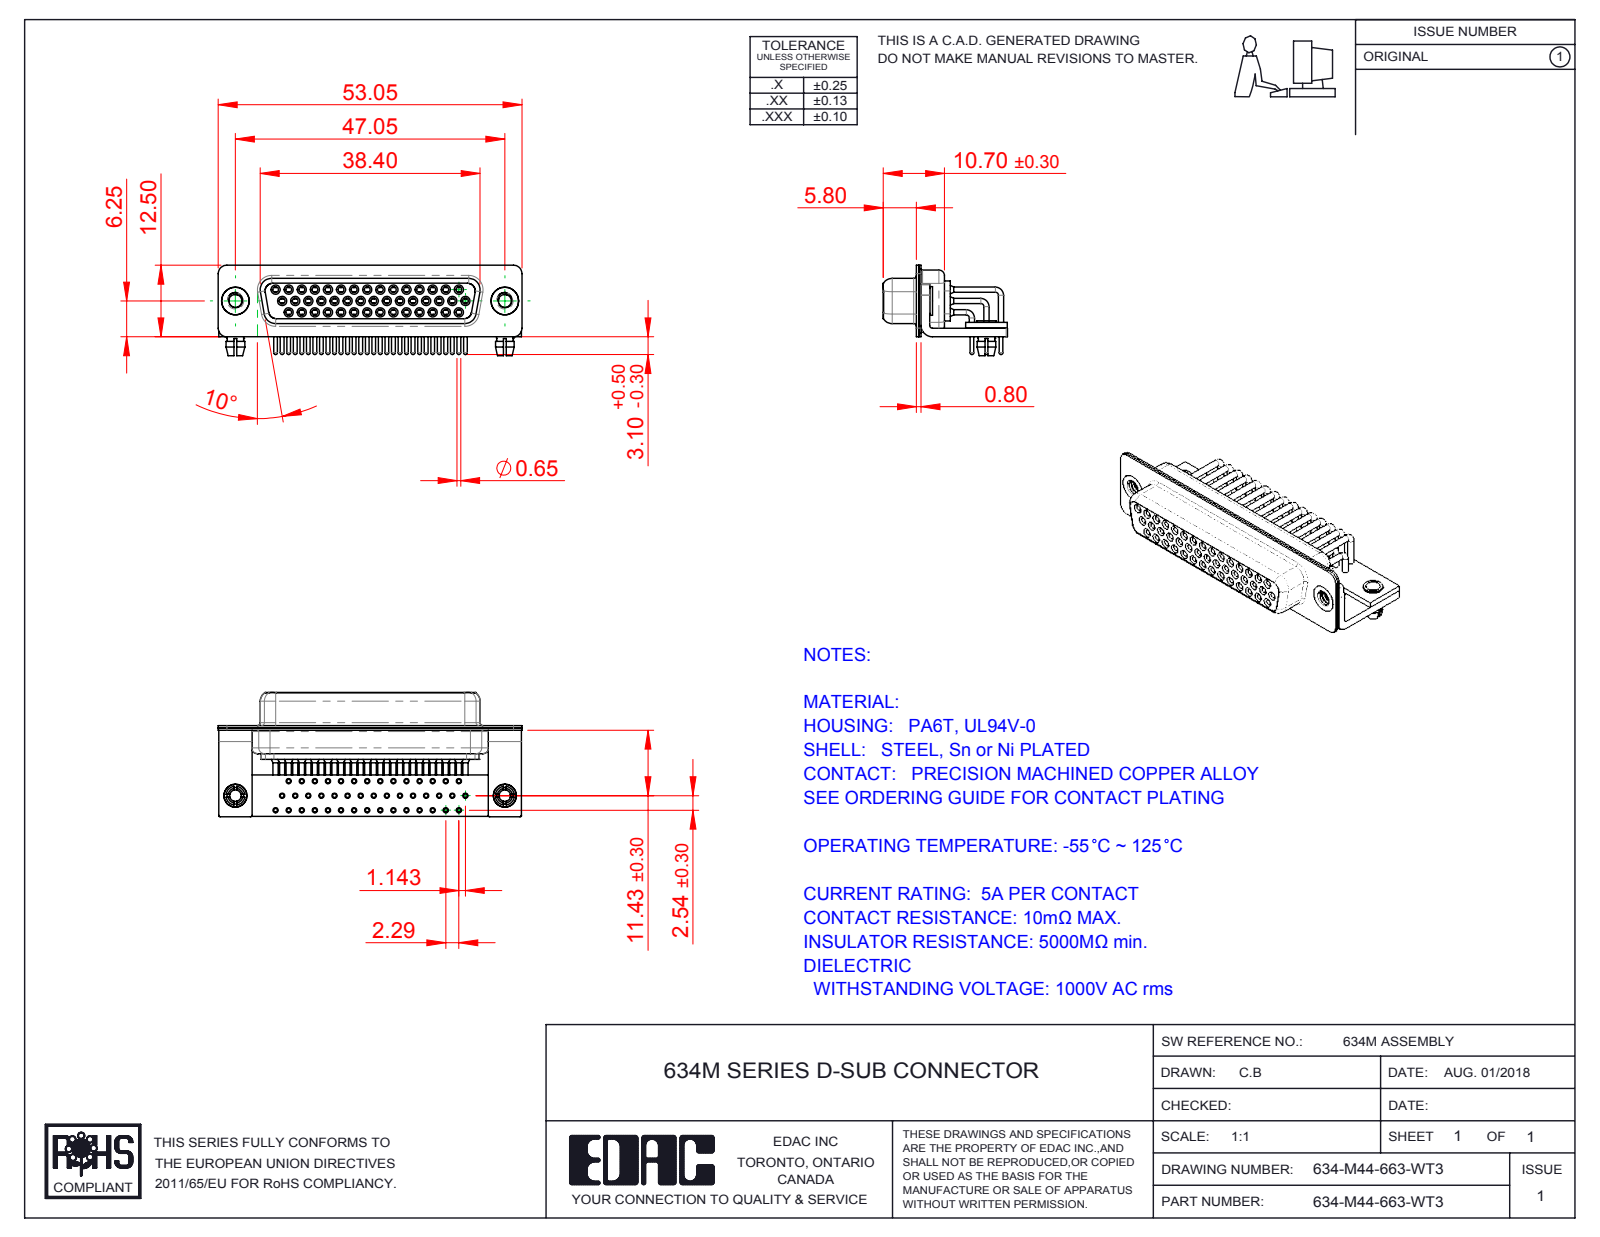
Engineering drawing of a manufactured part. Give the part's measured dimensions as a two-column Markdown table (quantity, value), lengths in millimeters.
| quantity | value |
| --- | --- |
| part name | 634M Housing_44 Contacts; 634-M44-663-WT3; 634M Board Lock; 634M Stabilizer Board_44 Contacts (+7 more) |
| STEP written by | SolidWorks 2016 (CONFIG_CONTROL_DESIGN) |
| units | millimeters |
| bodies | 54 solids, 2841 faces (801 planar, 1291 cylindrical, 749 other) |
| overall size | 53.05 × 21.7 × 15.8 |
| volume | 4 503 mm³ |
| surface area | 14 836 mm² |
| round holes (diameter × count) | 2 × 46, 0.9 × 44, 1 × 44, 1.1 × 44, 1.7 × 44, 1.8 × 44, 2.26 × 2, 2.5 × 2, 3.2 × 2, 4 × 2, 4.8 × 2 |
| round bosses / shafts (diameter × count) | 1.6 × 44, 1.5 × 44, 0.9 × 44, 0.65 × 44, 5 × 2, 4.9 × 2, 4 × 2, 3.4 × 2 |
| partial cylindrical surfaces (radius × count) | 0.25 × 16, 1.5 × 16, 2 × 13, 1.35 × 8, 1.6 × 8, 0.5 × 5, 0.6 × 4, 0.65 × 4 |
| main face-to-face distances | 0.4, 2.3, 1, 1.9, 0.8, 9.35, 1.45, 8.95, 1.5, 0.85 |
| hole center spacings | 2.28, 2.29, 4.57, 6.86, 11.43, 3.96, 8.24, 9.14 |
